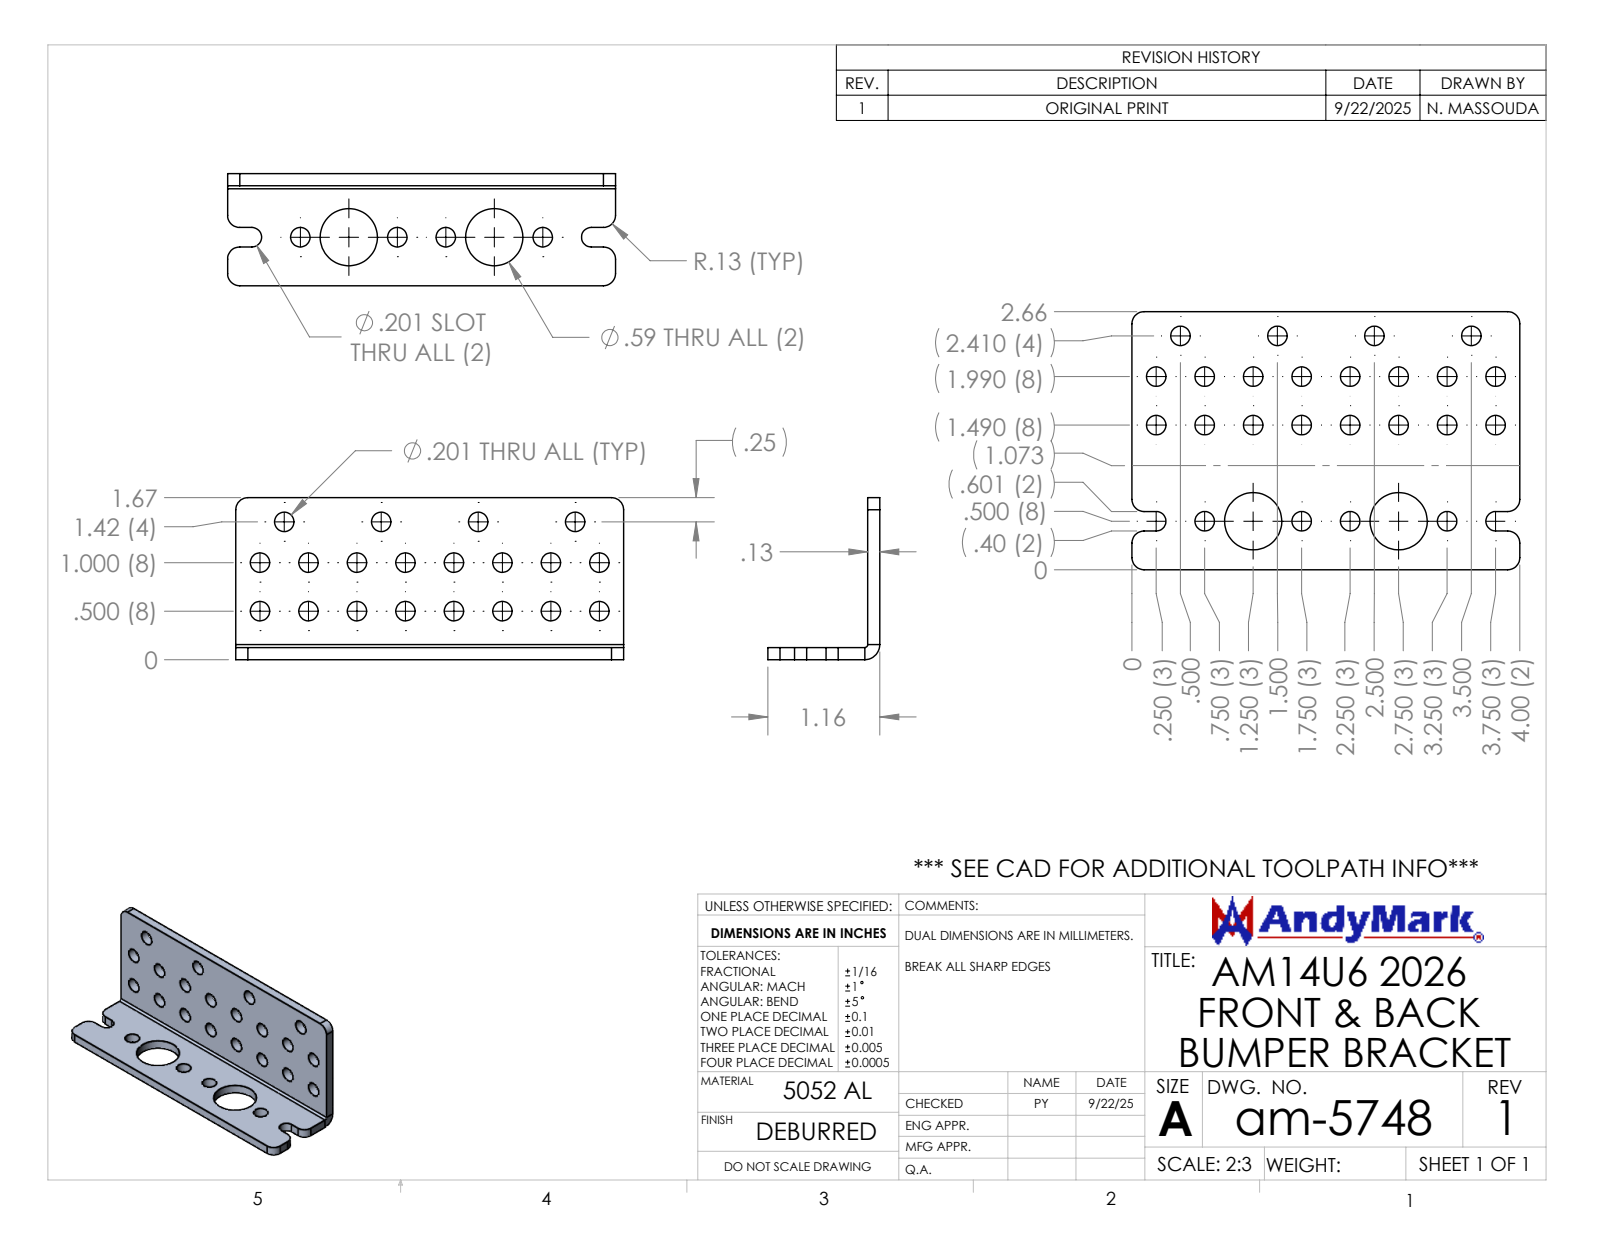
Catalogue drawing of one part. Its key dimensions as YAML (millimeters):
part_name: "am-5748 AM14U6 2026 Front Back Bumper Bracket"
step_written_by: "SolidWorks 2024 (CONFIG_CONTROL_DESIGN)"
units: millimeters
bodies: {solids: 1, faces: 82, planar: 18, cylindrical: 64, other: 0}
overall_size: [101.6, 42.4, 29.3]
volume: 18800
surface_area: 14500
round_holes:
  - {diameter: 5.1, count: 24}
  - {diameter: 15, count: 2}
partial_cylinders:
  - {radius: 3.2, count: 8}
  - {radius: 2.6, count: 2}
  - {radius: 0.8, count: 1}
  - {radius: 3.9, count: 1}
face_to_face_distances: [3.2, 29.3, 26.2, 42.4, 39.2, 101.6, 14.1, 10.9, 15.3, 19.2]
hole_center_spacings: [12.7, 25.4, 18, 38.1, 28.4, 50.8, 40.2, 12.4]
